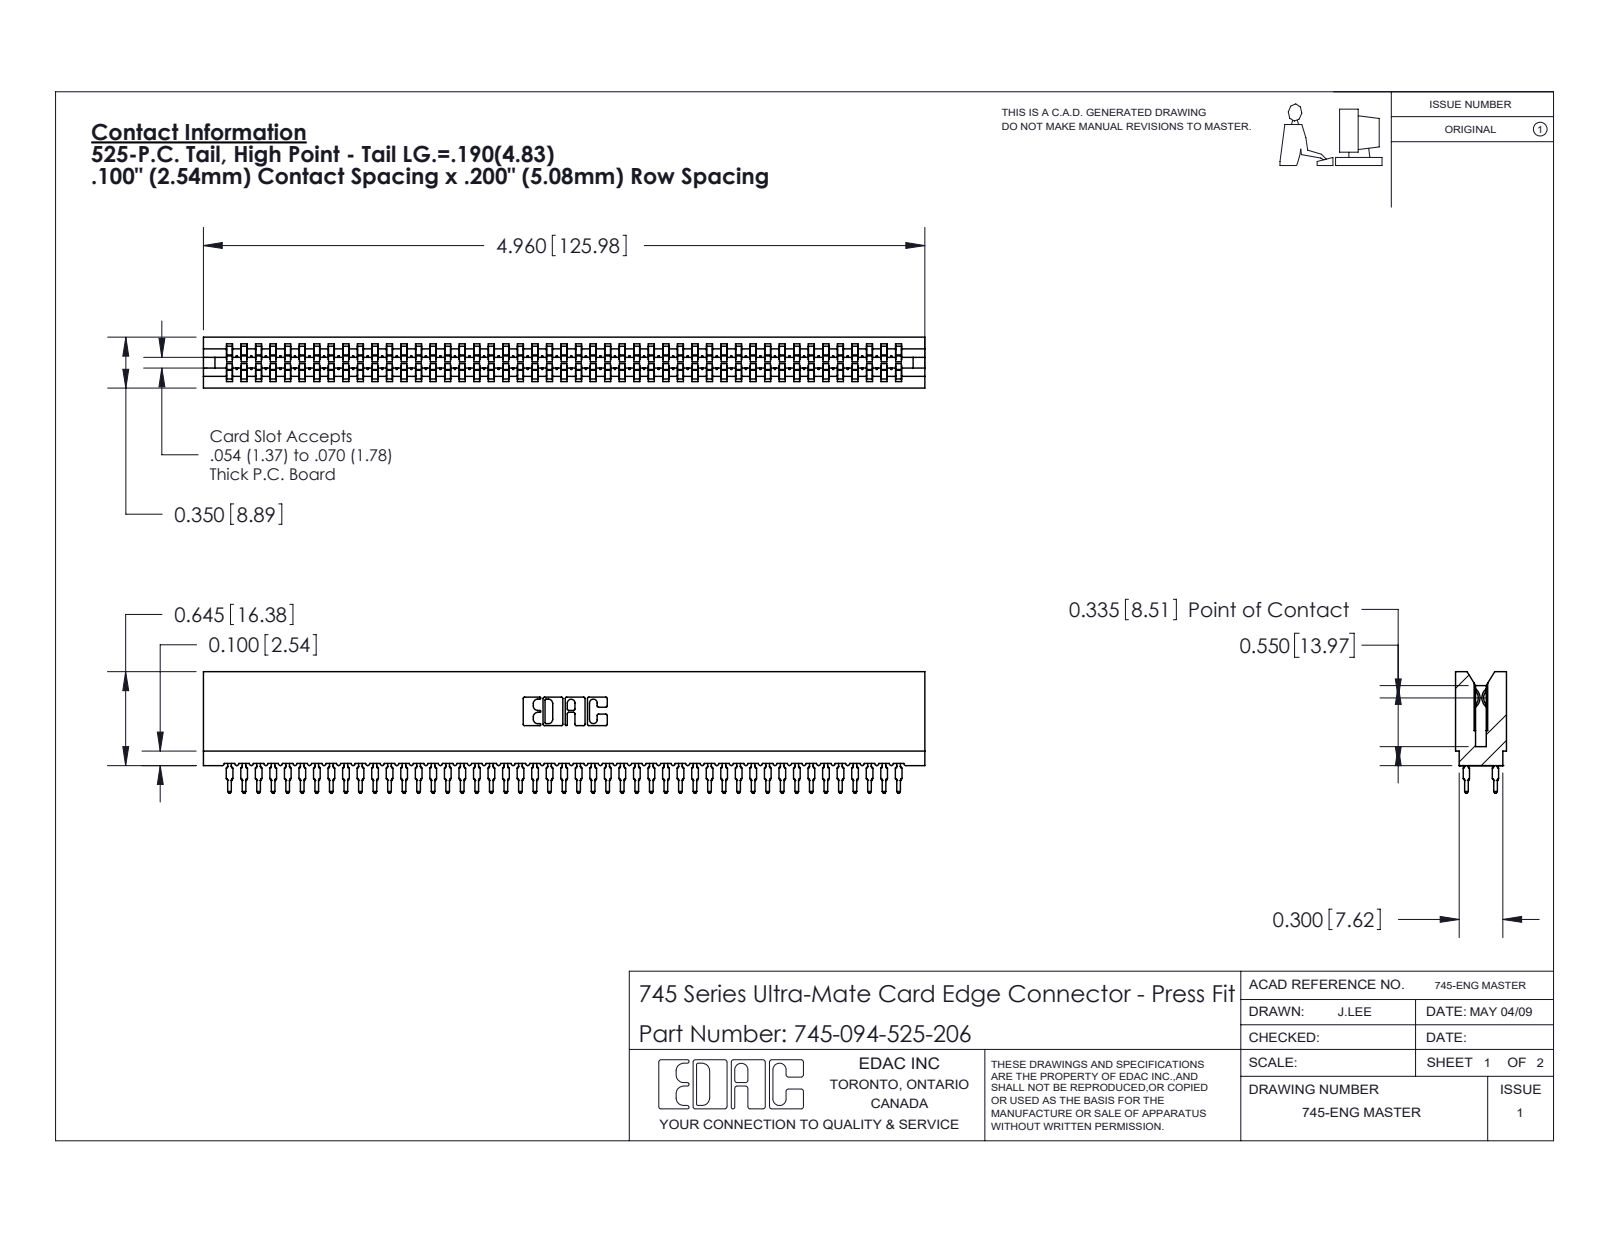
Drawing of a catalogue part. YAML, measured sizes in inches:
part_name: "745 Part_Insulator Option - 06; 745-292-001_525; 745-094-525-206"
step_written_by: "SolidWorks 2020 (CONFIG_CONTROL_DESIGN)"
units: inches
bodies: {solids: 95, faces: 8509, planar: 4380, cylindrical: 1685, other: 2444}
overall_size: [4.96, 0.836, 0.35]
volume: 0.688
surface_area: 35.59
partial_cylinders:
  - {radius: 0.021, count: 188}
  - {radius: 0.015, count: 94}
  - {radius: 0.01, count: 22}
  - {radius: 0.005, count: 8}
  - {radius: 0.011, count: 8}
  - {radius: 0.007, count: 6}
  - {radius: 0.031, count: 6}
  - {radius: 0.026, count: 3}
face_to_face_distances: [0.35, 0.063, 0.287, 0.045, 0.305, 0.018, 0.243, 0.138, 0.212, 0.093]
